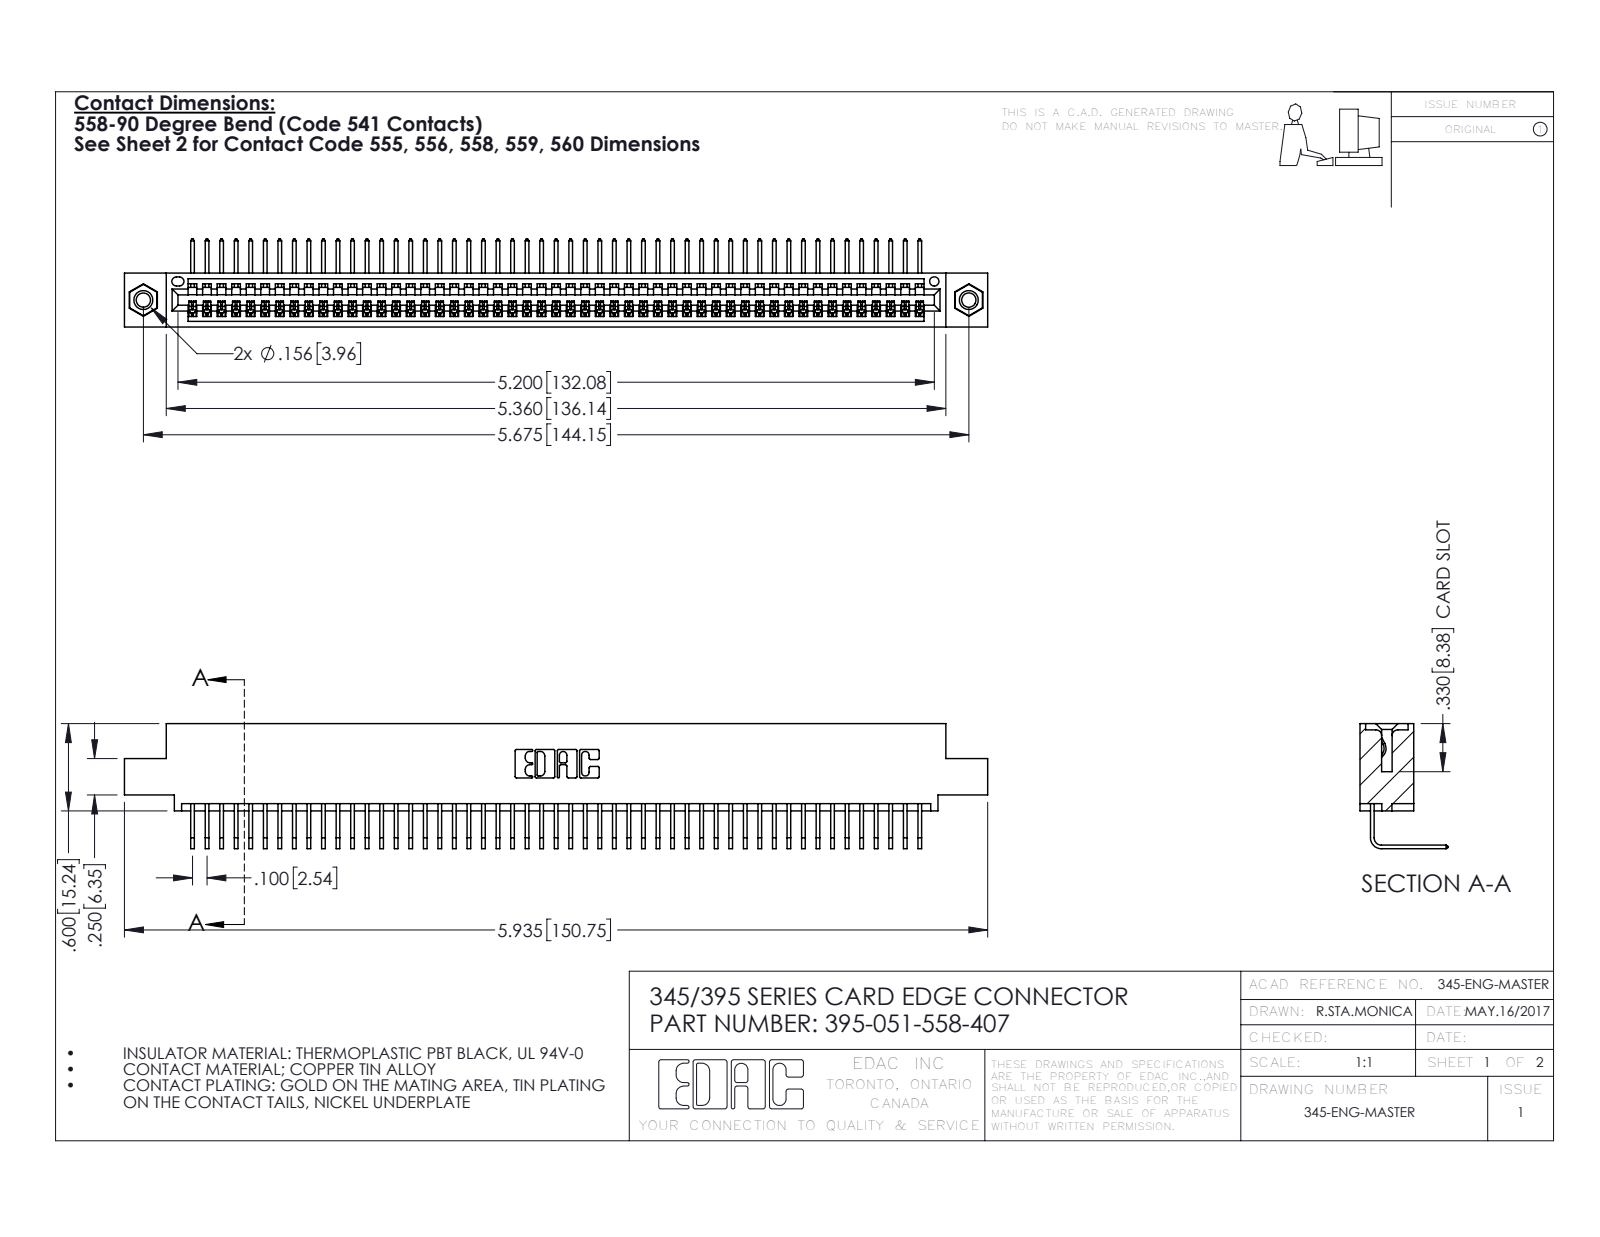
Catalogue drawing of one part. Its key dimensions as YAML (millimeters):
part_name: "345-250-001_345-250-005-103; 345 Part_0.110 Offset - 0.156 Dia-TI; 395-051-558-407; 345-292-001_558 Tail - 2"
step_written_by: "SolidWorks 2016 (CONFIG_CONTROL_DESIGN)"
units: millimeters
bodies: {solids: 54, faces: 3250, planar: 2258, cylindrical: 976, other: 16}
overall_size: [150.7, 21.8, 15.4]
volume: 14500
surface_area: 20470
round_holes:
  - {diameter: 2.5, count: 2}
  - {diameter: 3.2, count: 2}
  - {diameter: 4, count: 2}
  - {diameter: 1.6, count: 1}
round_bosses_or_shafts:
  - {diameter: 3.9, count: 2}
partial_cylinders:
  - {radius: 0.2, count: 102}
  - {radius: 0.3, count: 22}
  - {radius: 0.2, count: 6}
  - {radius: 0.8, count: 6}
  - {radius: 0.7, count: 3}
  - {radius: 0.8, count: 2}
  - {radius: 1, count: 2}
  - {radius: 0.4, count: 1}
face_to_face_distances: [1.8, 7.6, 9.4, 5.1, 2.5, 6.9, 0.6, 5.7, 3.8, 1.8]
hole_center_spacings: [6.9, 138.2, 144.1]
